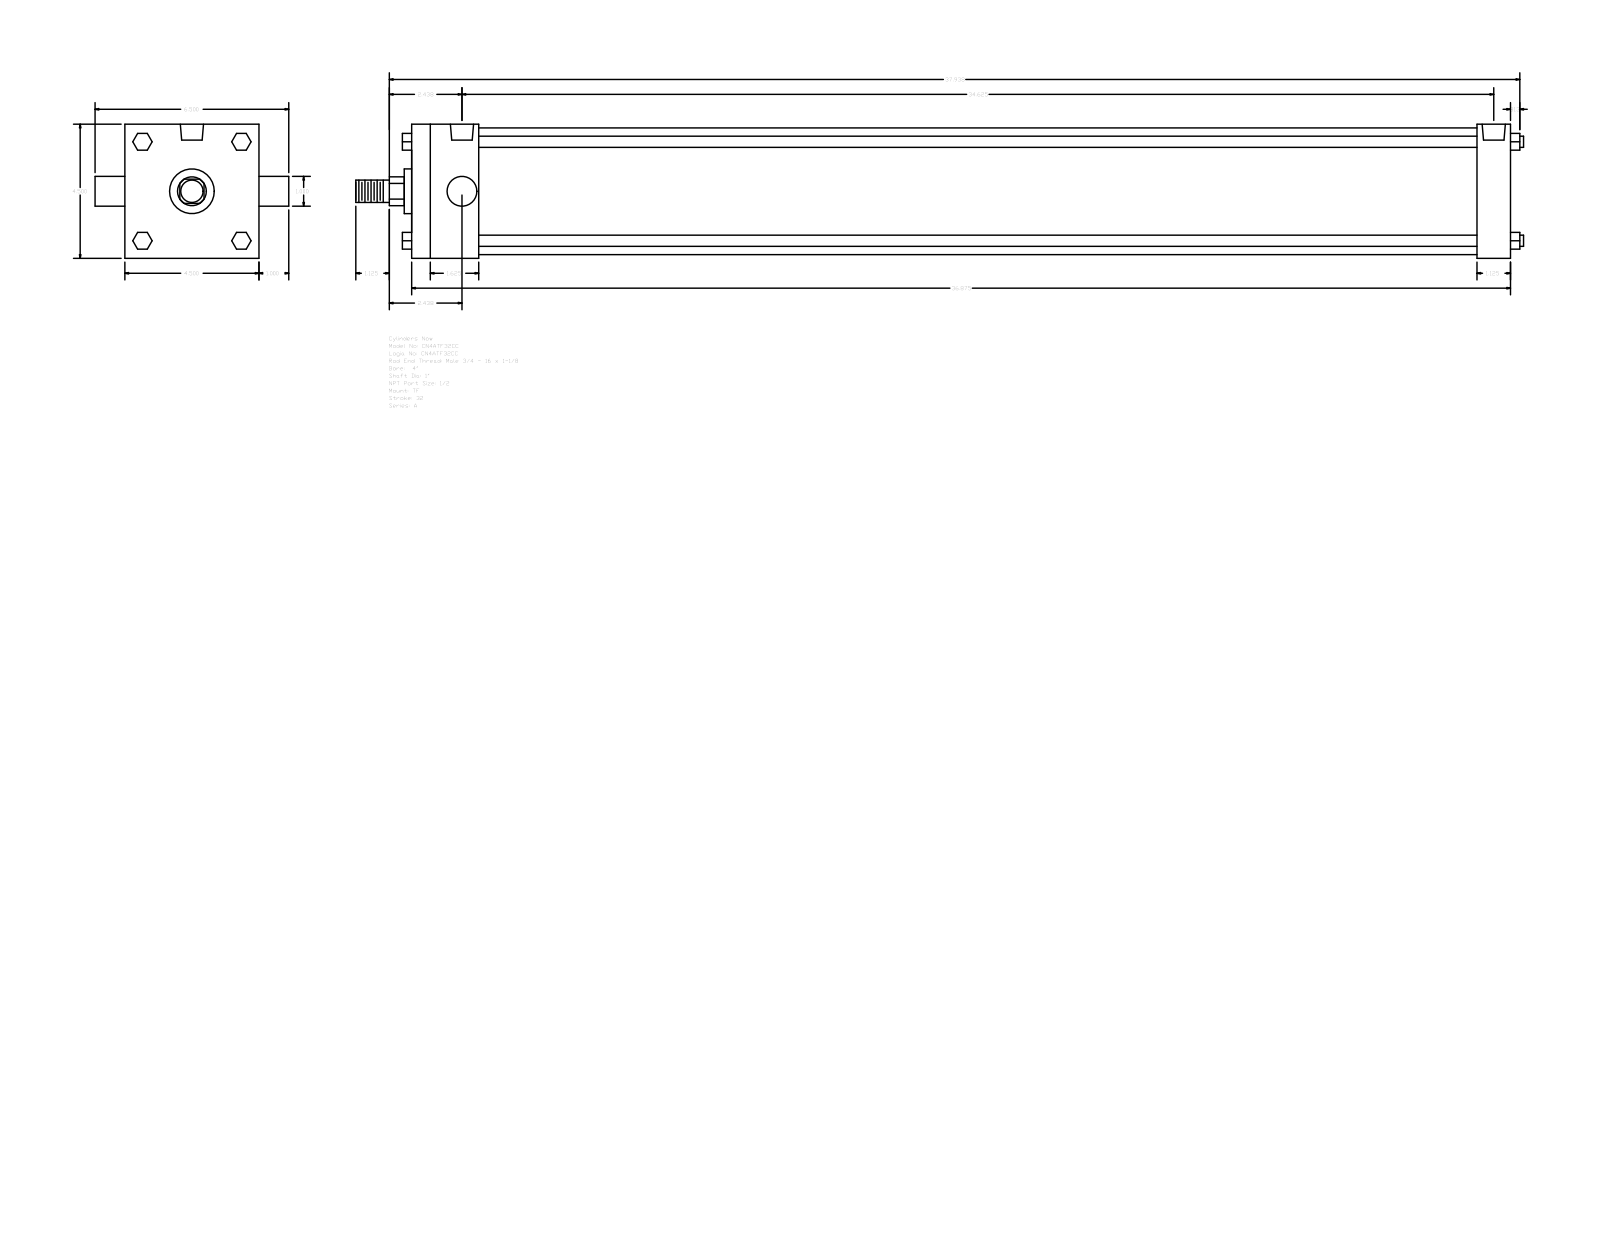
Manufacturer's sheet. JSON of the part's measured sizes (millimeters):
{"part_name": "A_TF__0400_1", "step_written_by": "GSSL Pune (CONFIG_CONTROL_DESIGN)", "units": "millimeters", "bodies": {"solids": 0, "faces": 120, "planar": 92, "cylindrical": 28, "other": 0}, "overall_size": [995.36, 165.1, 114.3], "round_holes": [[8.73, 3], [19.77, 2]], "round_bosses_or_shafts": [[9.53, 4], [25.4, 2], [107.95, 1], [38.1, 1], [19.05, 1]], "partial_cylinders_radius": [[12.29, 1]], "face_to_face_distances": [114.3, 936.62, 28.57, 908.05, 57.15, 850.9, 879.47, 14.29, 42.16, 73.03], "hole_center_spacings": [3.18, 876.3, 873.12, 879.48]}
